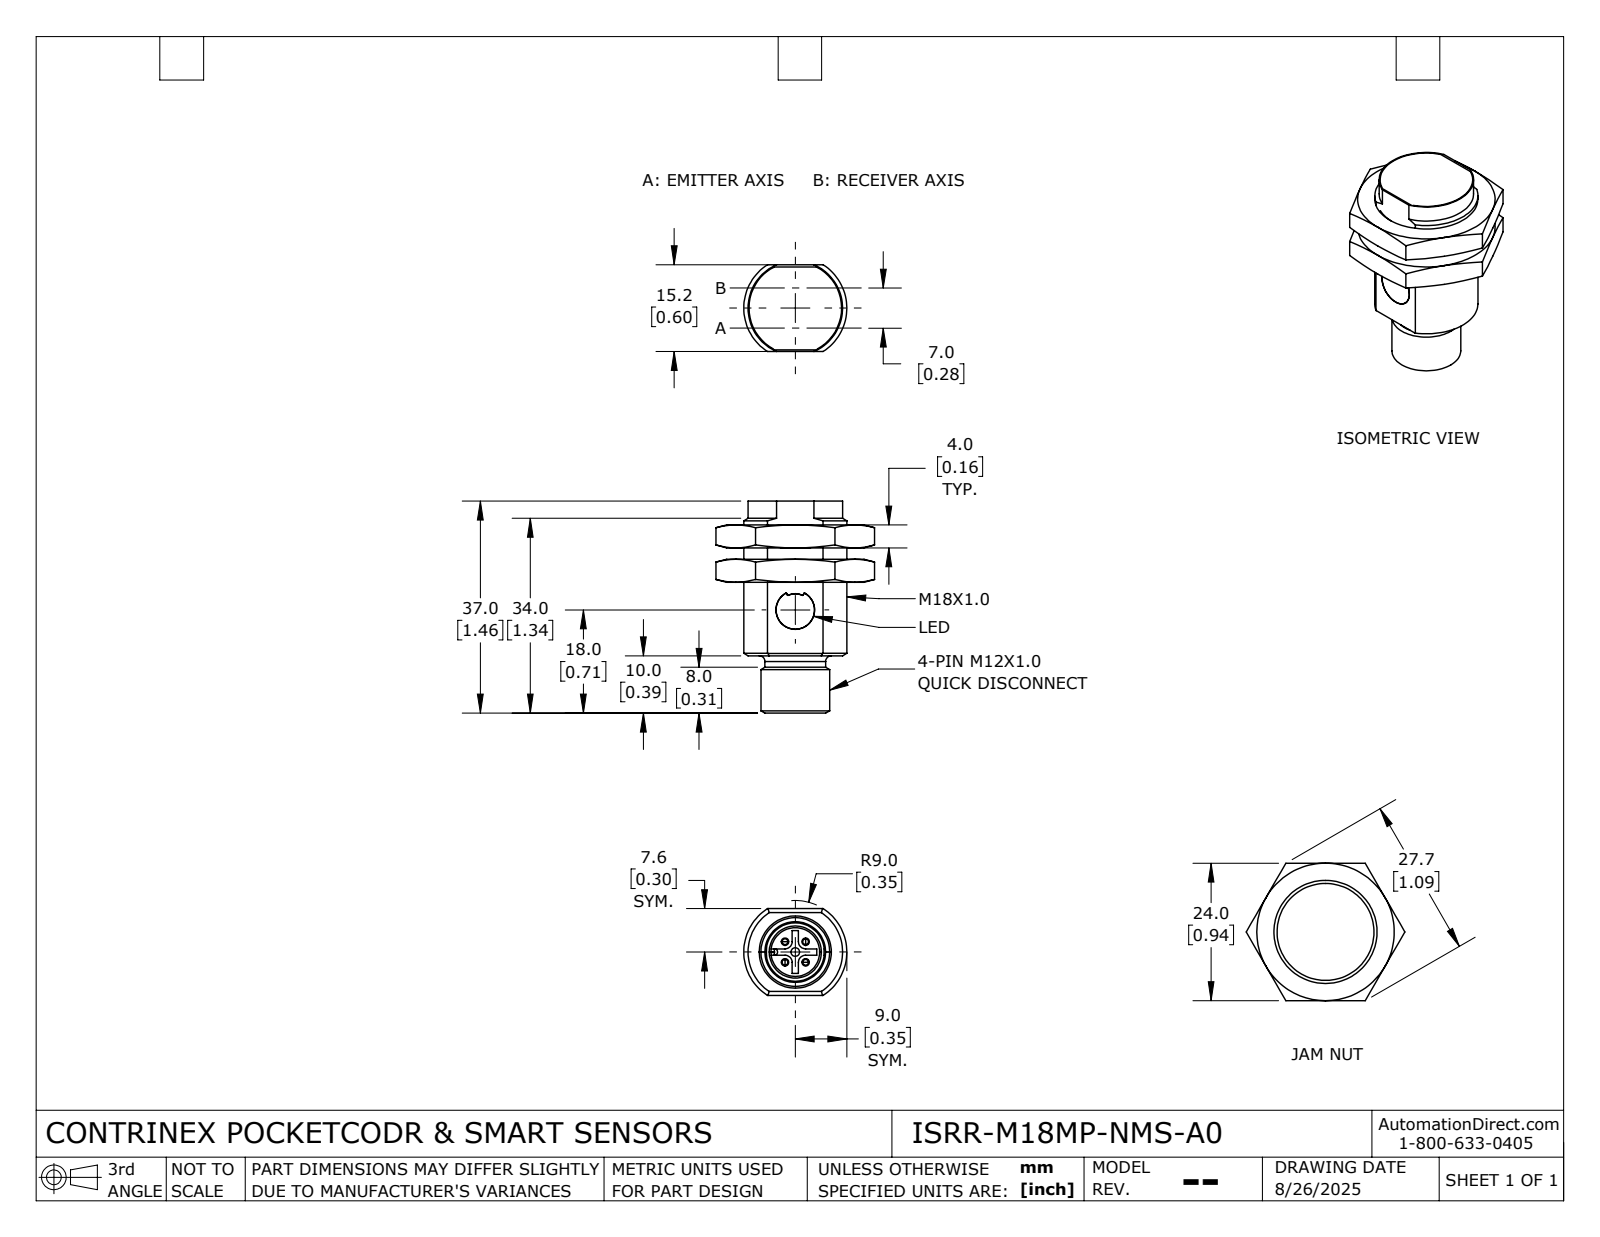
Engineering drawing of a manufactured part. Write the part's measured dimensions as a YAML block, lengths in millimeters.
part_name: "ISRR-M18MP-NMS-A0"
step_written_by: "SolidWorks 2024 (AUTOMOTIVE_DESIGN)"
units: millimeters
bodies: {solids: 3, faces: 157, planar: 67, cylindrical: 41, other: 49}
overall_size: [37, 27.7, 24]
volume: 9000
surface_area: 4736
round_holes:
  - {diameter: 1.5, count: 1}
  - {diameter: 6.8, count: 1}
  - {diameter: 8.5, count: 1}
  - {diameter: 16.9, count: 1}
round_bosses_or_shafts:
  - {diameter: 1, count: 4}
  - {diameter: 12, count: 1}
  - {diameter: 10.6, count: 1}
  - {diameter: 6.7, count: 1}
partial_cylinders:
  - {radius: 0.1, count: 4}
  - {radius: 1.2, count: 4}
  - {radius: 0.1, count: 2}
  - {radius: 0.5, count: 2}
  - {radius: 0.6, count: 1}
  - {radius: 2.8, count: 1}
  - {radius: 2.8, count: 1}
  - {radius: 8.3, count: 1}
face_to_face_distances: [6, 4, 24, 15.2, 10, 4.4, 19.6, 10.2, 4.2, 14.1]
